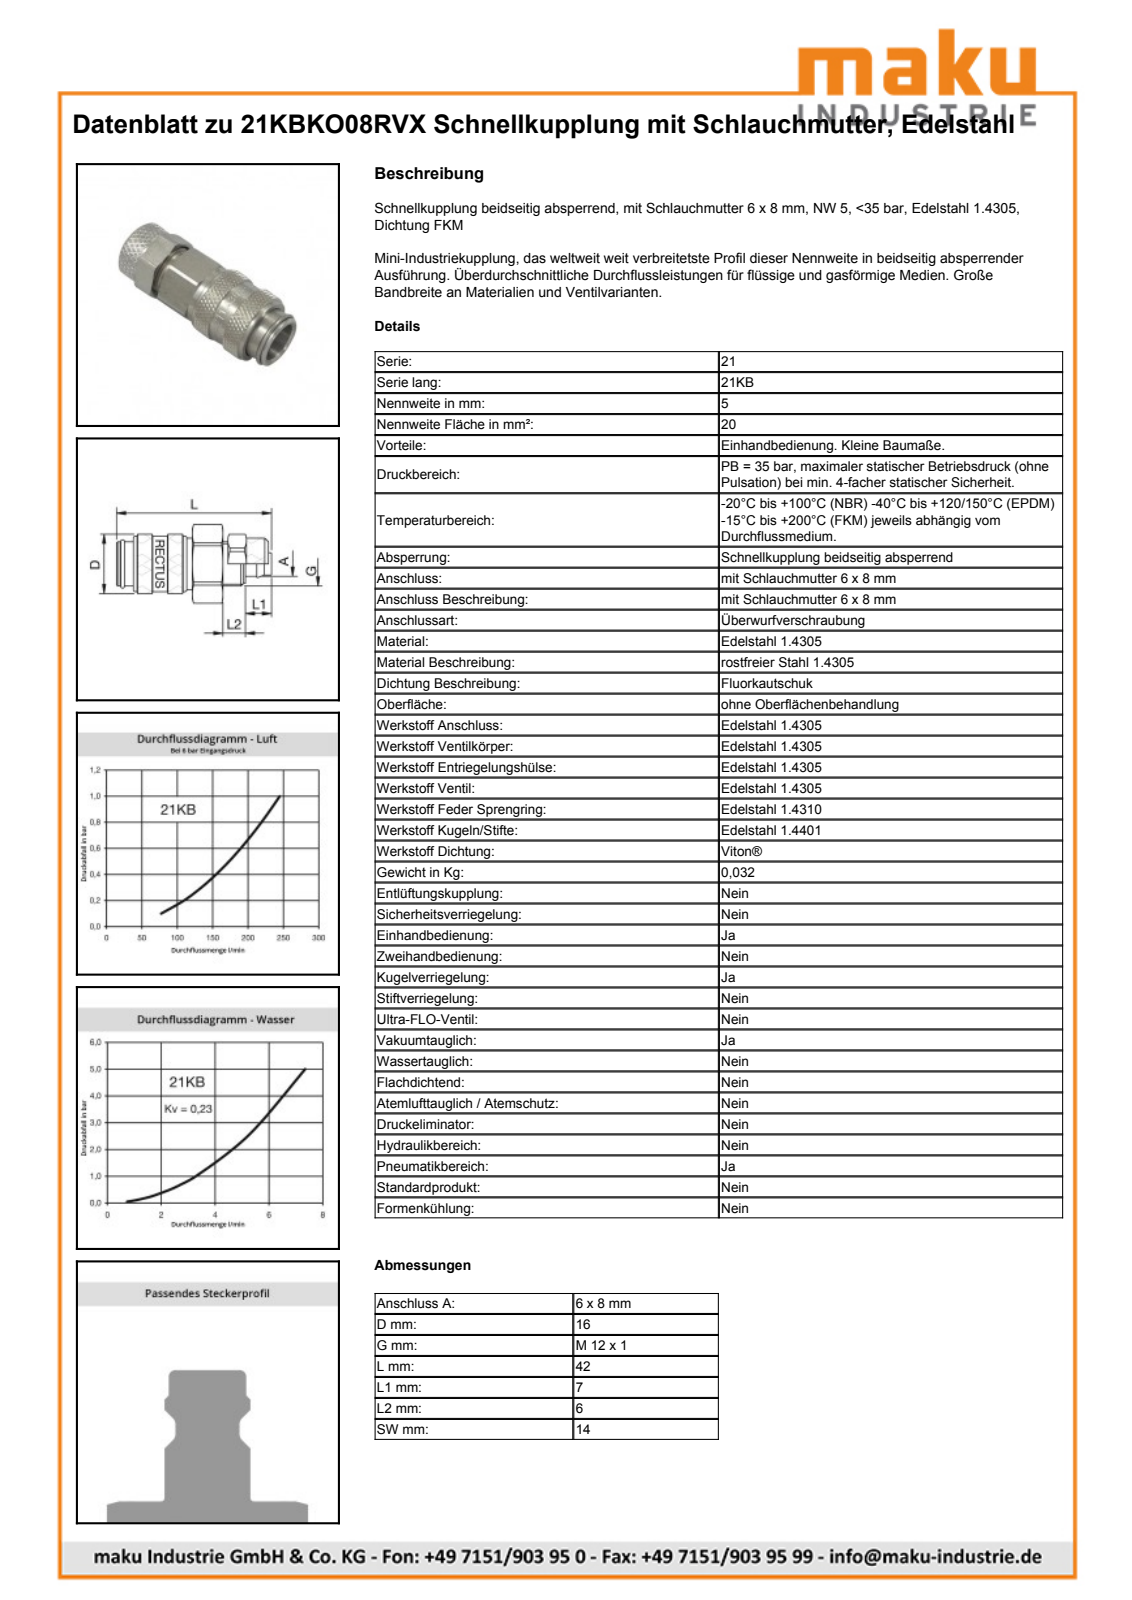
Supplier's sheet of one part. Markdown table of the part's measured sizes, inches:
| quantity | value |
| --- | --- |
| part name | D105922 |
| STEP written by | Autodesk Inventor 2011 (AUTOMOTIVE_DESIGN) |
| units | inches |
| bodies | 2 solids, 442 faces (140 planar, 74 cylindrical, 228 other) |
| overall size | 1.659 × 0.636 × 0.636 |
| volume | 0.373 in³ |
| surface area | 6.863 in² |
| round holes (diameter × count) | 0.433 × 1, 0.476 × 1, 0.478 × 1, 0.492 × 1, 0.496 × 1, 0.551 × 1 |
| round bosses / shafts (diameter × count) | 0.636 × 1, 0.594 × 1, 0.472 × 1, 0.449 × 1, 0.439 × 1, 0.423 × 1, 0.409 × 1, 0.264 × 1 |
| partial cylindrical surfaces (radius × count) | 0.293 × 1, 0.305 × 1, 0.311 × 1 |
| main face-to-face distances | 0.551, 0.043, 0.476, 1.38, 1.14, 0.24, 0.197, 1.616, 0.236, 0.547 |
